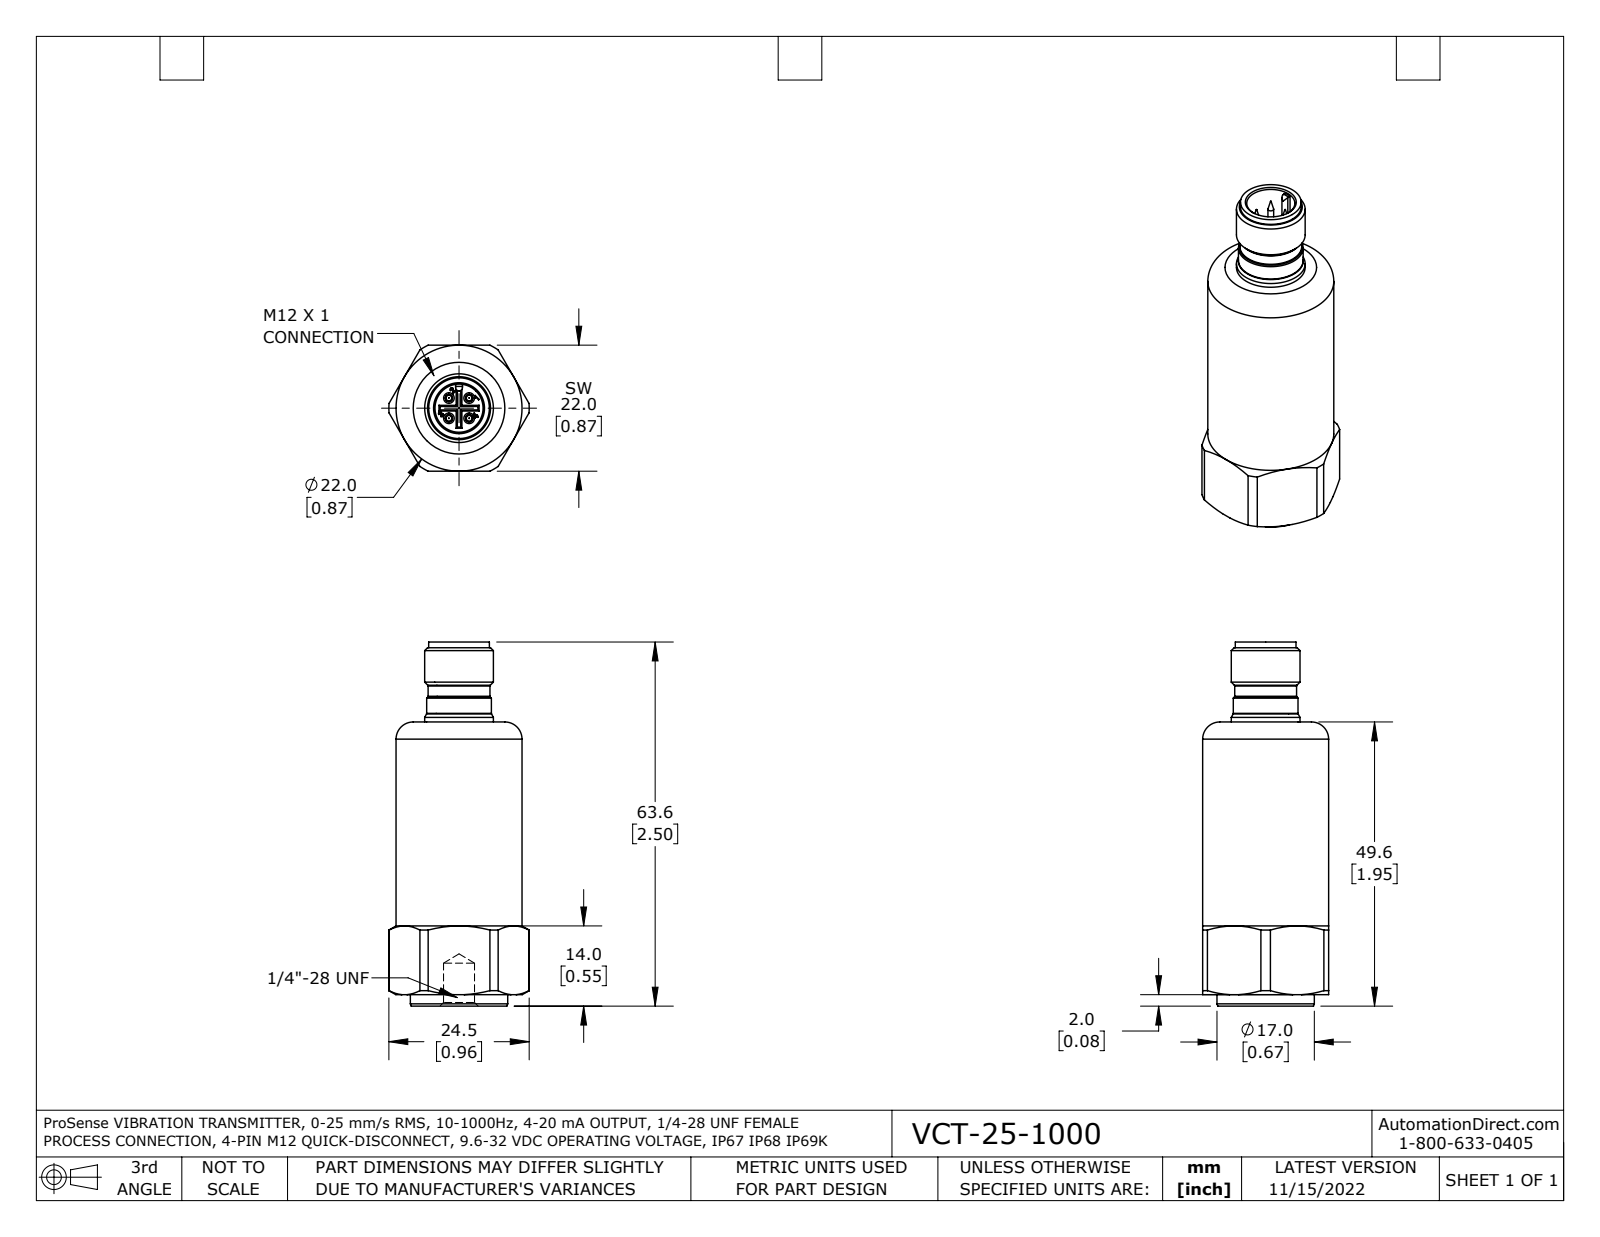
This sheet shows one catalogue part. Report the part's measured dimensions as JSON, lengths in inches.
{"part_name": "VTC002_3D", "step_written_by": "SolidWorks 2021 (AUTOMOTIVE_DESIGN)", "units": "inches", "bodies": {"solids": 1, "faces": 218, "planar": 62, "cylindrical": 61, "other": 95}, "overall_size": [2.502, 0.965, 0.866], "volume_in3": 1.199, "surface_area_in2": 8.001, "round_holes": [[0.049, 4], [0.213, 1], [0.331, 1]], "round_bosses_or_shafts": [[0.047, 4], [0.039, 4], [0.866, 1], [0.669, 1], [0.472, 1], [0.445, 1], [0.425, 1], [0.417, 1]], "partial_cylinders_radius": [[0.008, 7], [0.024, 1], [0.031, 1], [0.482, 1]], "face_to_face_distances": [0.866, 0.079, 1.953, 1.874, 2.152, 2.073, 0.199, 0.35, 2.502, 2.423], "hole_center_spacings": [0.098, 0.139, 0.197]}
